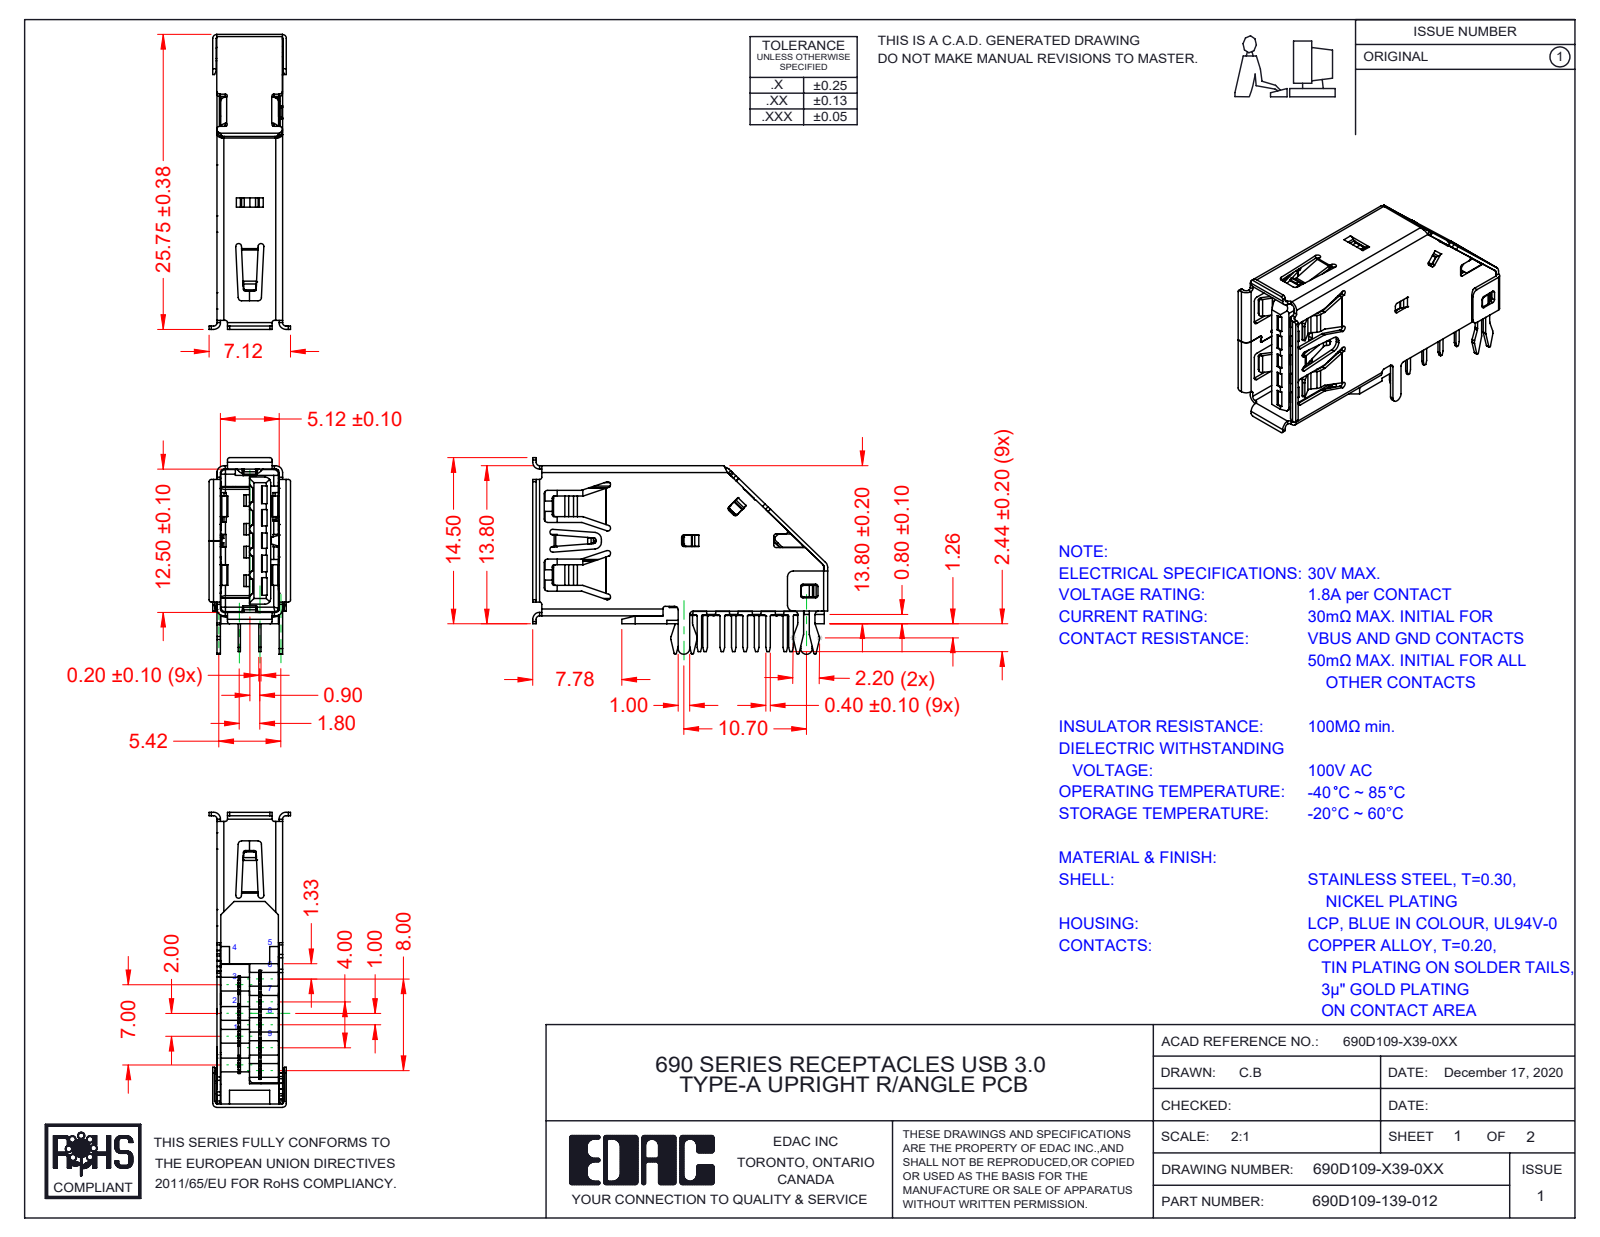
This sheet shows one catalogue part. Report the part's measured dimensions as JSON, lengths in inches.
{"part_name": "Insulator 2 690D109-X39-0XX_Blue; Contact 2.0 1 690D109-X39-0XX; Contact 2.0 4 690D109-X39-0XX; 690D109-139-012 (+8 more)", "step_written_by": "SolidWorks 2020 (AUTOMOTIVE_DESIGN)", "units": "inches", "bodies": {"solids": 13, "faces": 2780, "planar": 1938, "cylindrical": 770, "other": 72}, "overall_size": [1.014, 0.676, 0.28], "volume_in3": 0.063, "surface_area_in2": 6.71, "round_holes": [[0.031, 1]], "partial_cylinders_radius": [[0.012, 78], [0.008, 76], [0.004, 66], [0.006, 43], [0.02, 36], [0.024, 30], [0.016, 24], [0.005, 18]], "face_to_face_distances": [0.213, 0.112, 0.031, 0.1, 0.102, 0.225, 0.113, 0.202, 0.039, 0.071]}
